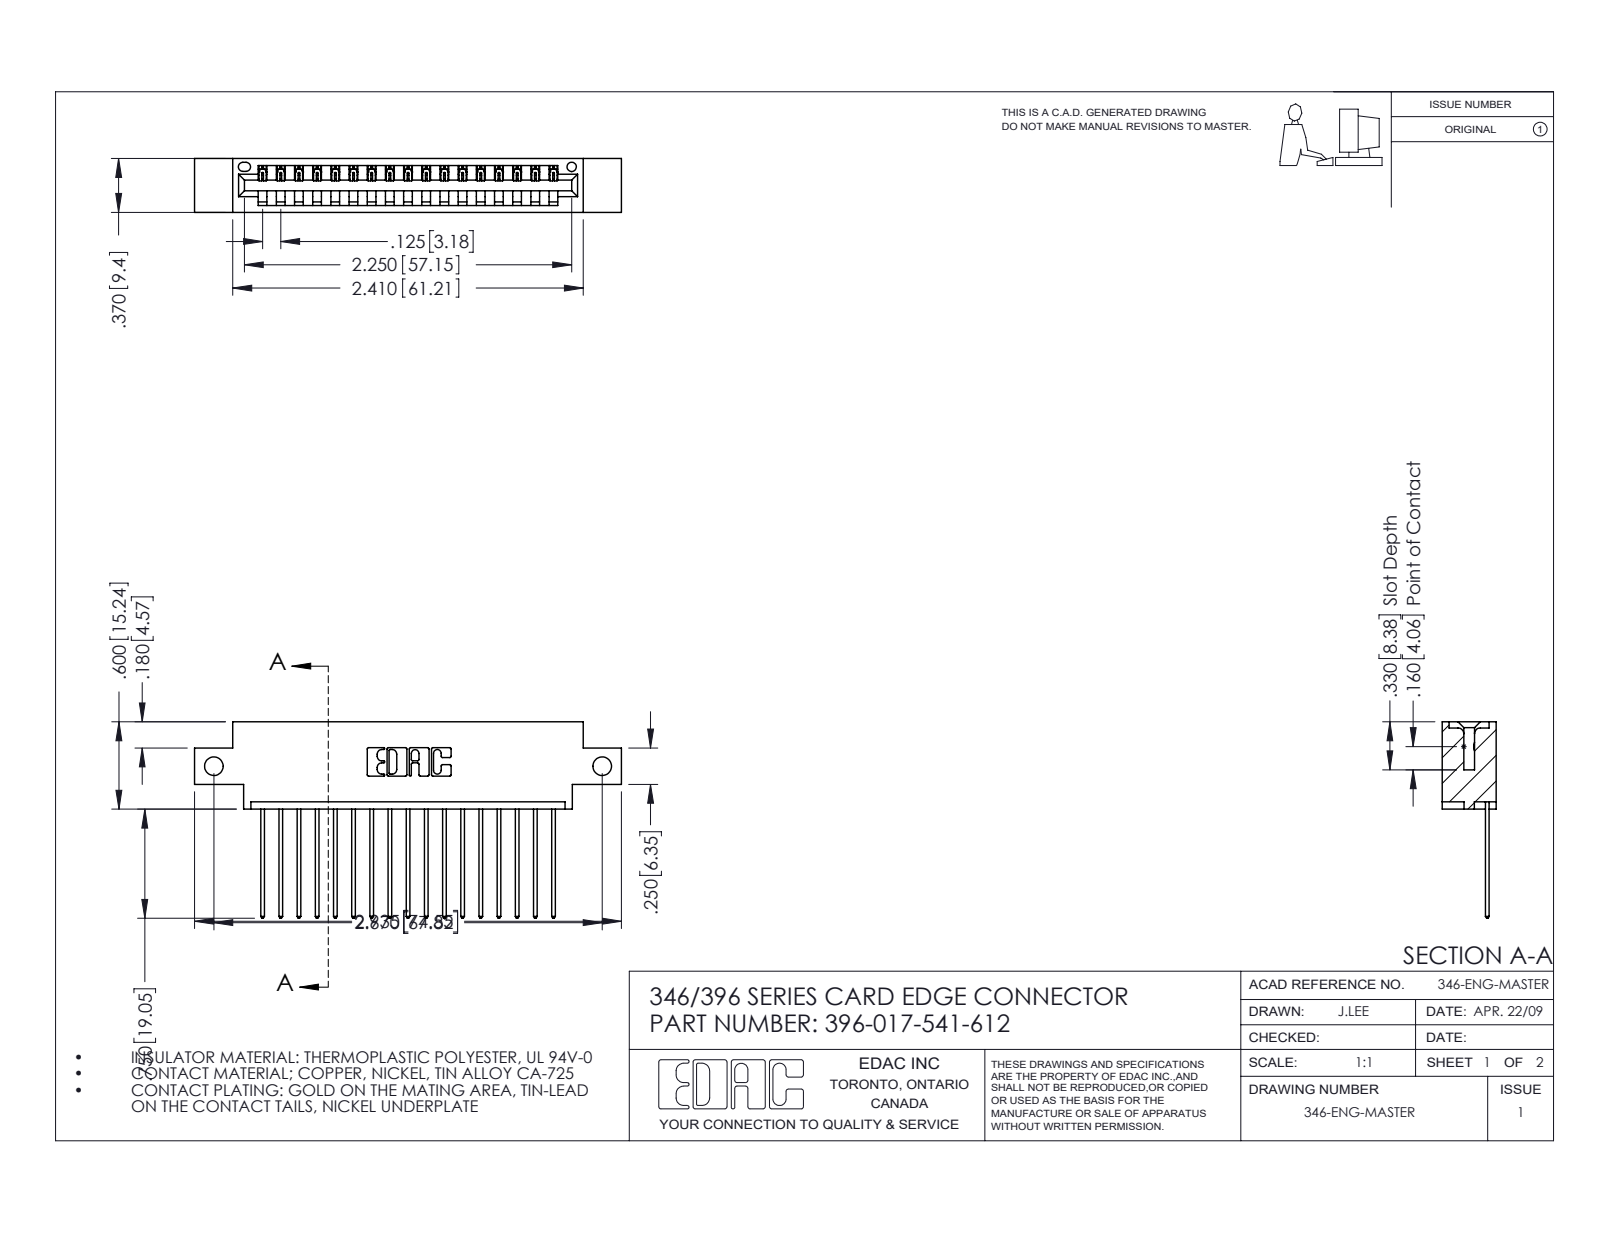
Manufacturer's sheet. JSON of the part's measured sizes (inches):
{"part_name": "396-017-541-612; 345-292-001_345-293-141; 346 Part_0.170 Offset - Side Mount", "step_written_by": "SolidWorks 2016 (CONFIG_CONTROL_DESIGN)", "units": "inches", "bodies": {"solids": 18, "faces": 1112, "planar": 760, "cylindrical": 352, "other": 0}, "overall_size": [2.935, 1.35, 0.37], "volume_in3": 0.414, "surface_area_in2": 13.25, "round_holes": [[0.128, 2], [0.064, 1]], "partial_cylinders_radius": [[0.006, 34], [0.01, 34], [0.01, 22], [0.007, 6], [0.031, 6], [0.026, 3], [0.031, 2], [0.04, 2]], "face_to_face_distances": [0.048, 0.322, 0.37, 0.25, 0.072, 0.298, 0.025, 0.148, 0.222, 0.1], "hole_center_spacings": [2.67]}
